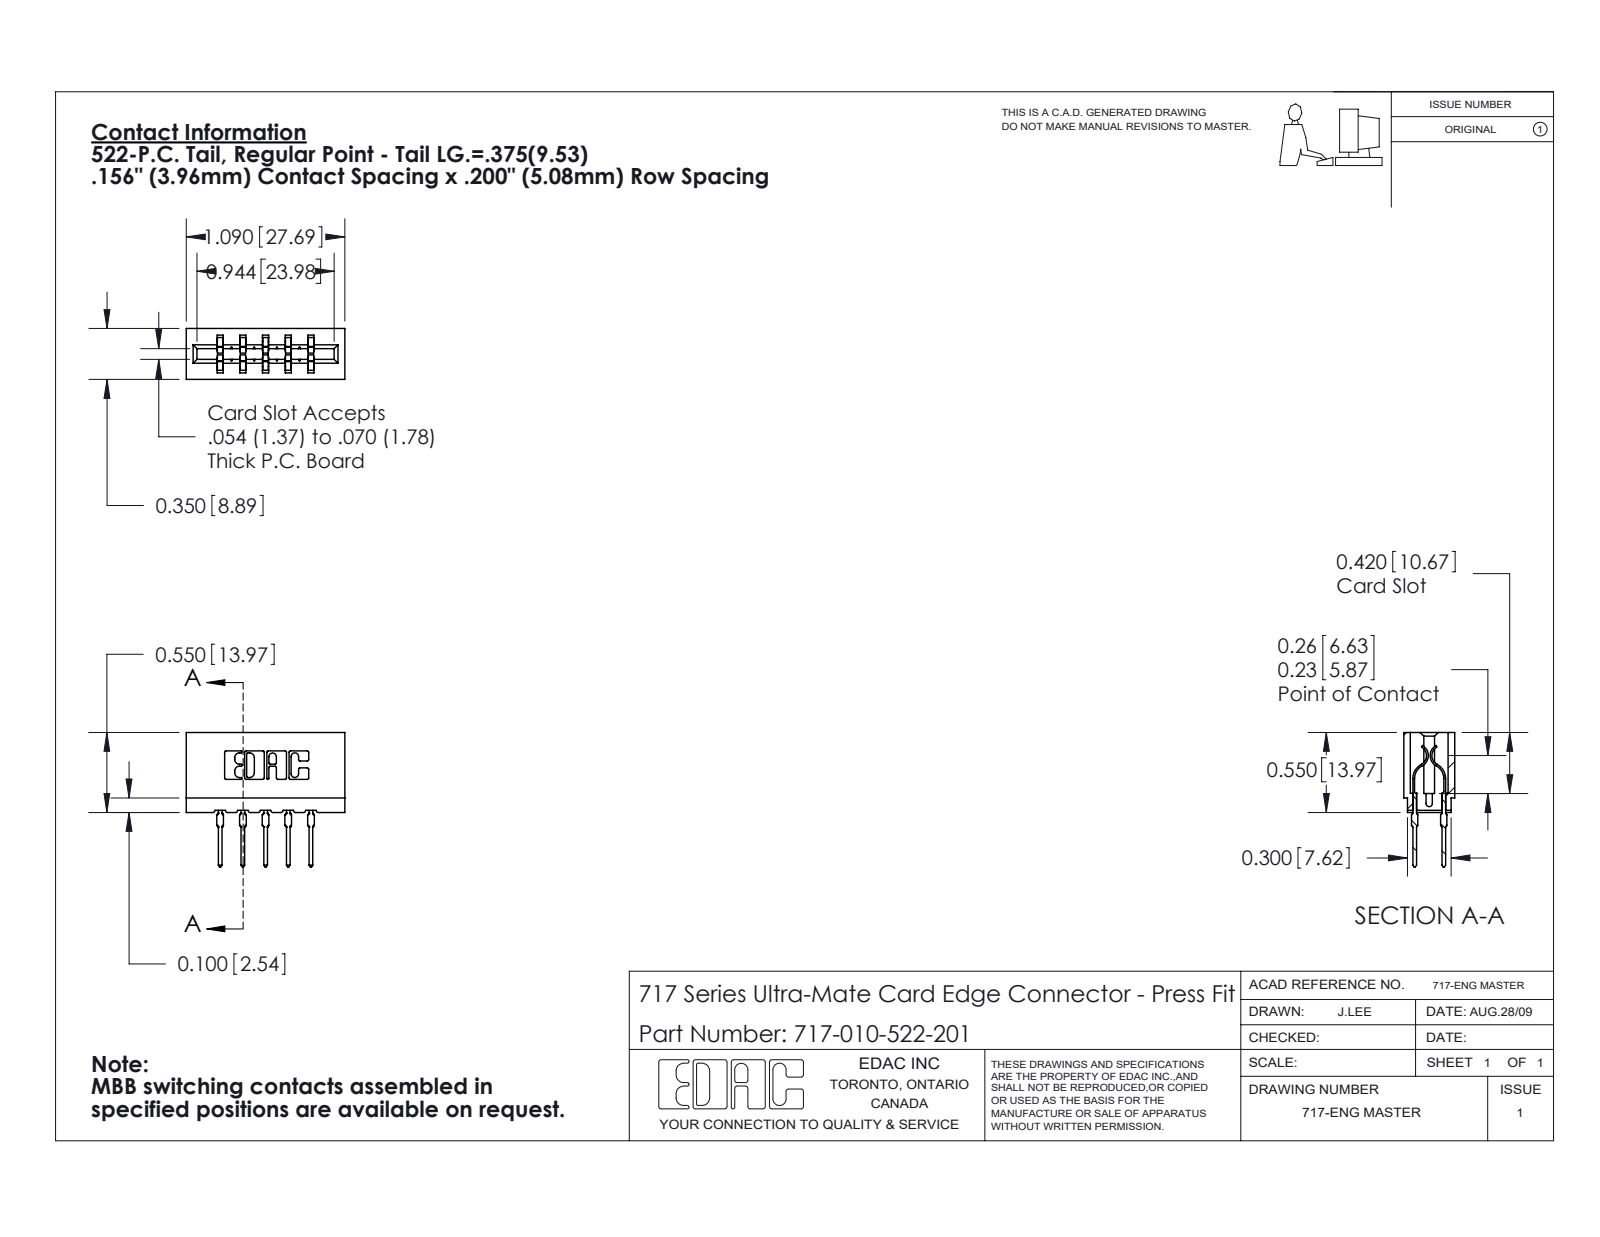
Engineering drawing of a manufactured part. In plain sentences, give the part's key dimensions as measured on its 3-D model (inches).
The part is named "745-292-001_522; 717-010-522-201; 717 Part_Insulator Option - 06". Its 3-D file was written by "SolidWorks 2020 (CONFIG_CONTROL_DESIGN)". It is 11 solids with 994 faces: 519 planar, 215 cylindrical and 260 other. Overall it measures 1.09 by 0.924 by 0.35 inches. Its volume is 0.156 cubic inches and its surface area 5.367 square inches. Partial cylindrical surfaces (rounded edges, fillets, slot ends): 22 of radius 0.01, 20 of radius 0.021, 10 of radius 0.015, 8 of radius 0.005, 8 of radius 0.011, 6 of radius 0.007, 6 of radius 0.031, 3 of radius 0.026. The main face-to-face distances are 0.212, 0.156, 0.138, 0.35, 0.198, 0.042, 0.312, 0.312, 0.468, 0.074.
